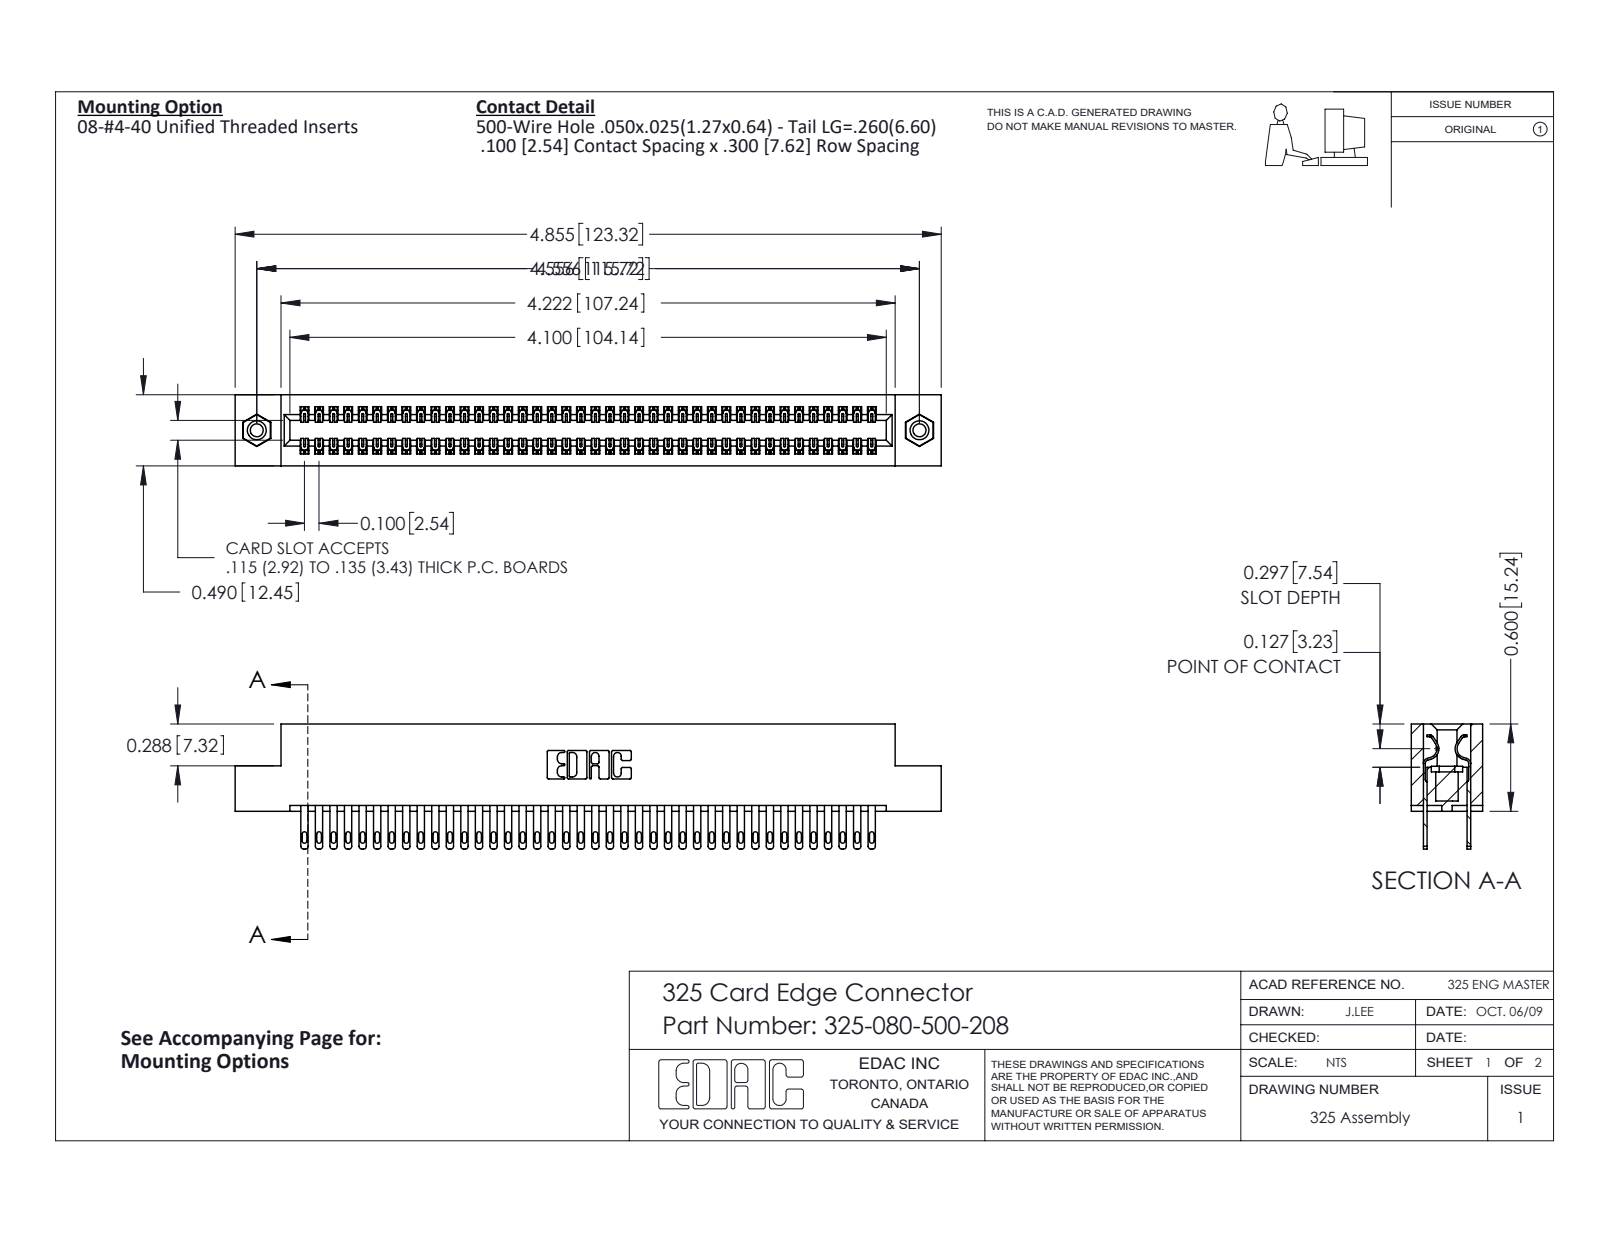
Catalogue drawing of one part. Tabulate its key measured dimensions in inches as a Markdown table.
| quantity | value |
| --- | --- |
| part name | 325-080-500-208; 345-250-001_345-250-003-102; 325 Part_TI; 325-292-001_325-293-100 |
| STEP written by | SolidWorks 2016 (CONFIG_CONTROL_DESIGN) |
| units | inches |
| bodies | 83 solids, 4014 faces (2502 planar, 1496 cylindrical, 16 other) |
| overall size | 4.855 × 0.86 × 0.49 |
| volume | 0.985 in³ |
| surface area | 31.52 in² |
| round holes (diameter × count) | 0.089 × 2, 0.125 × 2, 0.16 × 2 |
| round bosses / shafts (diameter × count) | 0.155 × 2 |
| partial cylindrical surfaces (radius × count) | 0.006 × 120, 0.016 × 80, 0.02 × 80, 0.01 × 22, 0.007 × 6, 0.031 × 6, 0.026 × 3, 0.014 × 2 |
| main face-to-face distances | 0.083, 0.407, 0.3, 0.107, 0.383, 0.025, 0.49, 0.325, 0.275, 0.56 |
| hole center spacings | 4.556 |
